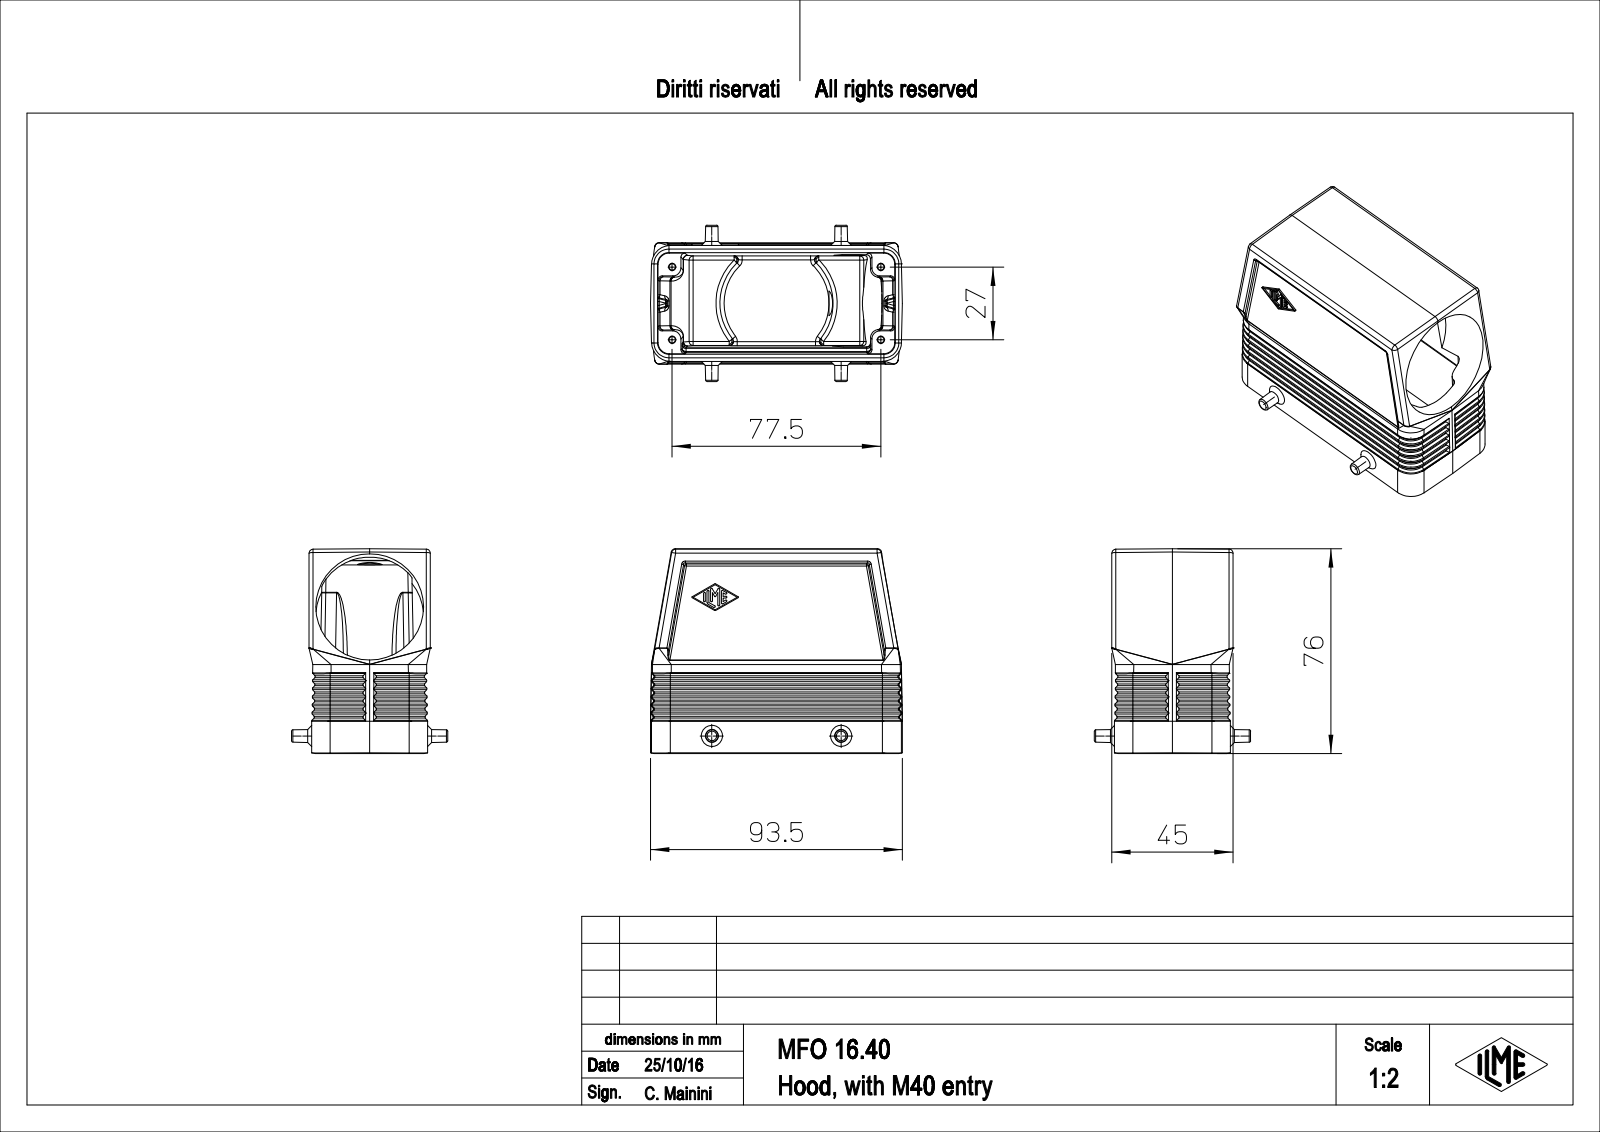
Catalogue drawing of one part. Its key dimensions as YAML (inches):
part_name: "MFO_16.40"
step_written_by: "PTC Creo Elements/Direct Modeling 19.0E 27-Jun-2016 (C) Parametric Technology GmbH (AUTOMOTIVE_DESIGN)"
units: inches
bodies: {solids: 1, faces: 481, planar: 212, cylindrical: 133, other: 136}
overall_size: [3.681, 2.992, 2.283]
volume: 5.093
surface_area: 67
round_holes:
  - {diameter: 0.108, count: 4}
  - {diameter: 1.575, count: 1}
round_bosses_or_shafts:
  - {diameter: 0.181, count: 2}
partial_cylinders:
  - {radius: 0.02, count: 78}
  - {radius: 0.059, count: 10}
  - {radius: 0.276, count: 8}
  - {radius: 0.118, count: 4}
  - {radius: 0.165, count: 4}
  - {radius: 0.827, count: 1}
face_to_face_distances: [1.693, 0.079, 0.079, 0.335, 0.157, 0.126, 0.039, 1.732, 0.236, 0.237]
hole_center_spacings: [1.063, 3.051, 3.231]
